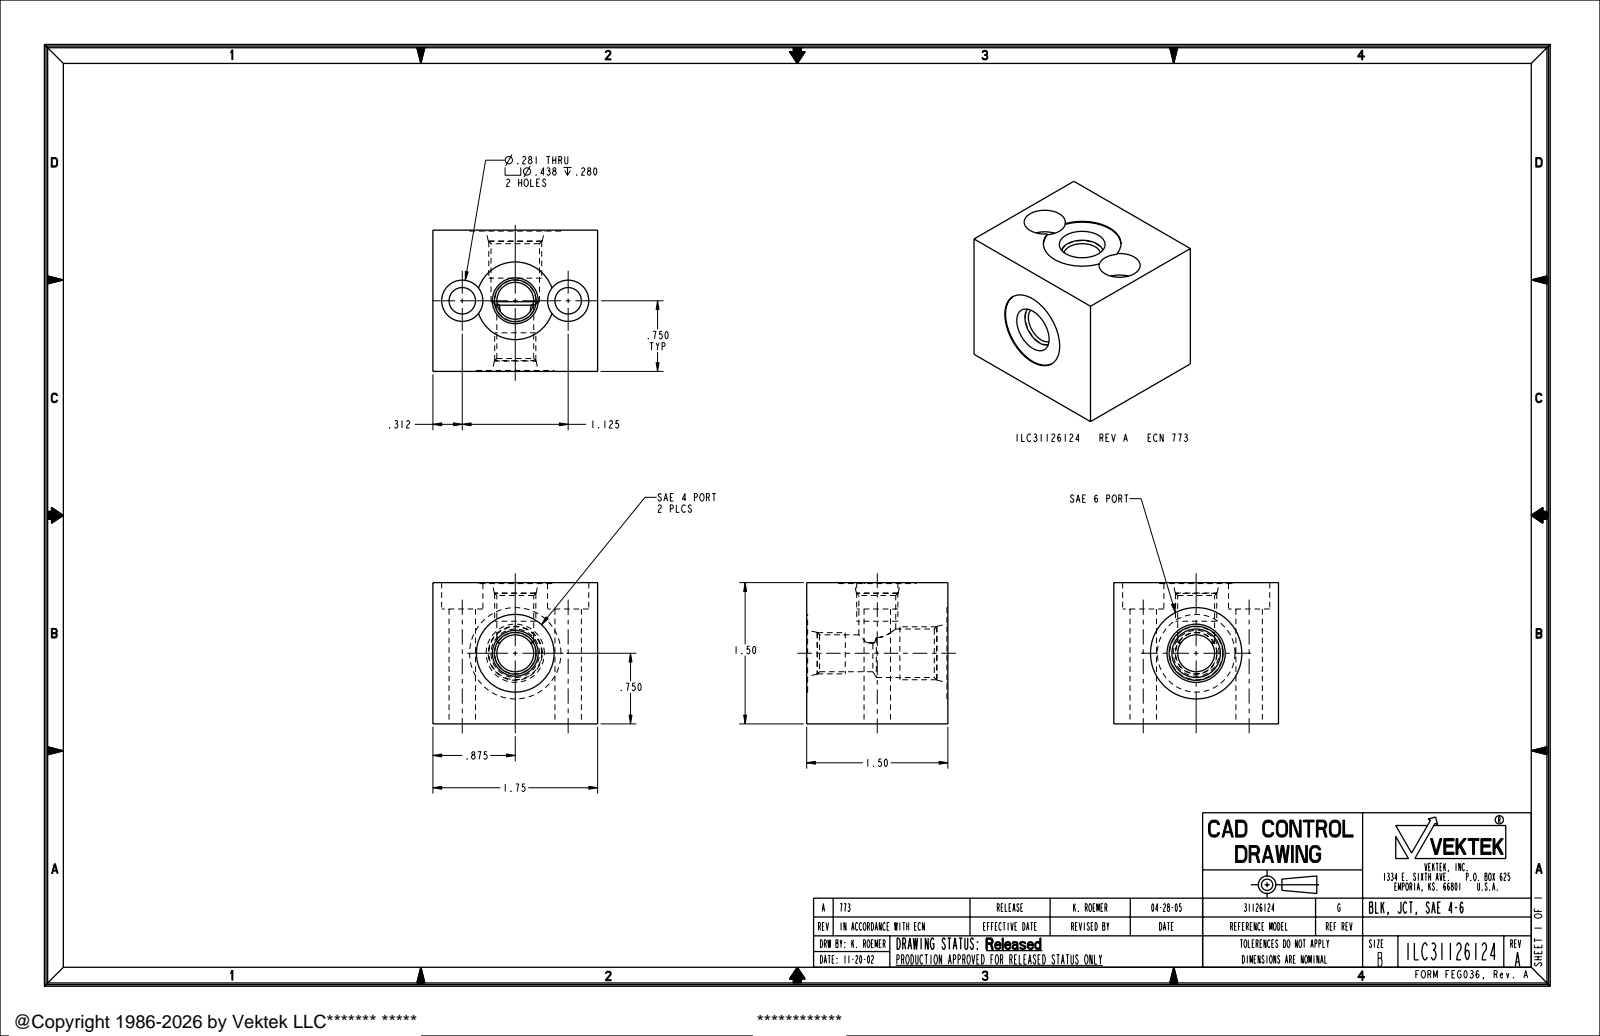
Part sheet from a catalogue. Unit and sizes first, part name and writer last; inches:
Units: inches
Overall size (bounding box): 1.75 × 1.5 × 1.5
Round holes (diameter × count): ⌀0.281 ×2, ⌀0.392 ×2, ⌀0.438 ×2, ⌀0.515 ×1, ⌀0.825 ×1, ⌀0.97 ×1
Round bosses / shafts (diameter × count): ⌀0.437 ×2, ⌀0.563 ×1
Partial cylindrical surfaces — rounded edges, fillets, slot ends (radius × count): R0.412 ×1
Main face-to-face distances: 1.5, 1.75, 1.49, 1.48, 1.22, 0.27, 0.28, 1.09, 0.4, 0.41
Hole centre spacings: 0.562, 0.563, 1.125
Volume: 3.355 in³ · Surface area: 21.53 in²
Bodies: 1 solid, 55 faces (14 planar, 26 cylindrical, 15 other)
Part name (STEP PRODUCT): ILC31126124
STEP written by: PRO/ENGINEER BY PARAMETRIC TECHNOLOGY CORPORATION, 2004290 (AUTOMOTIVE_DESIGN_CC2)
